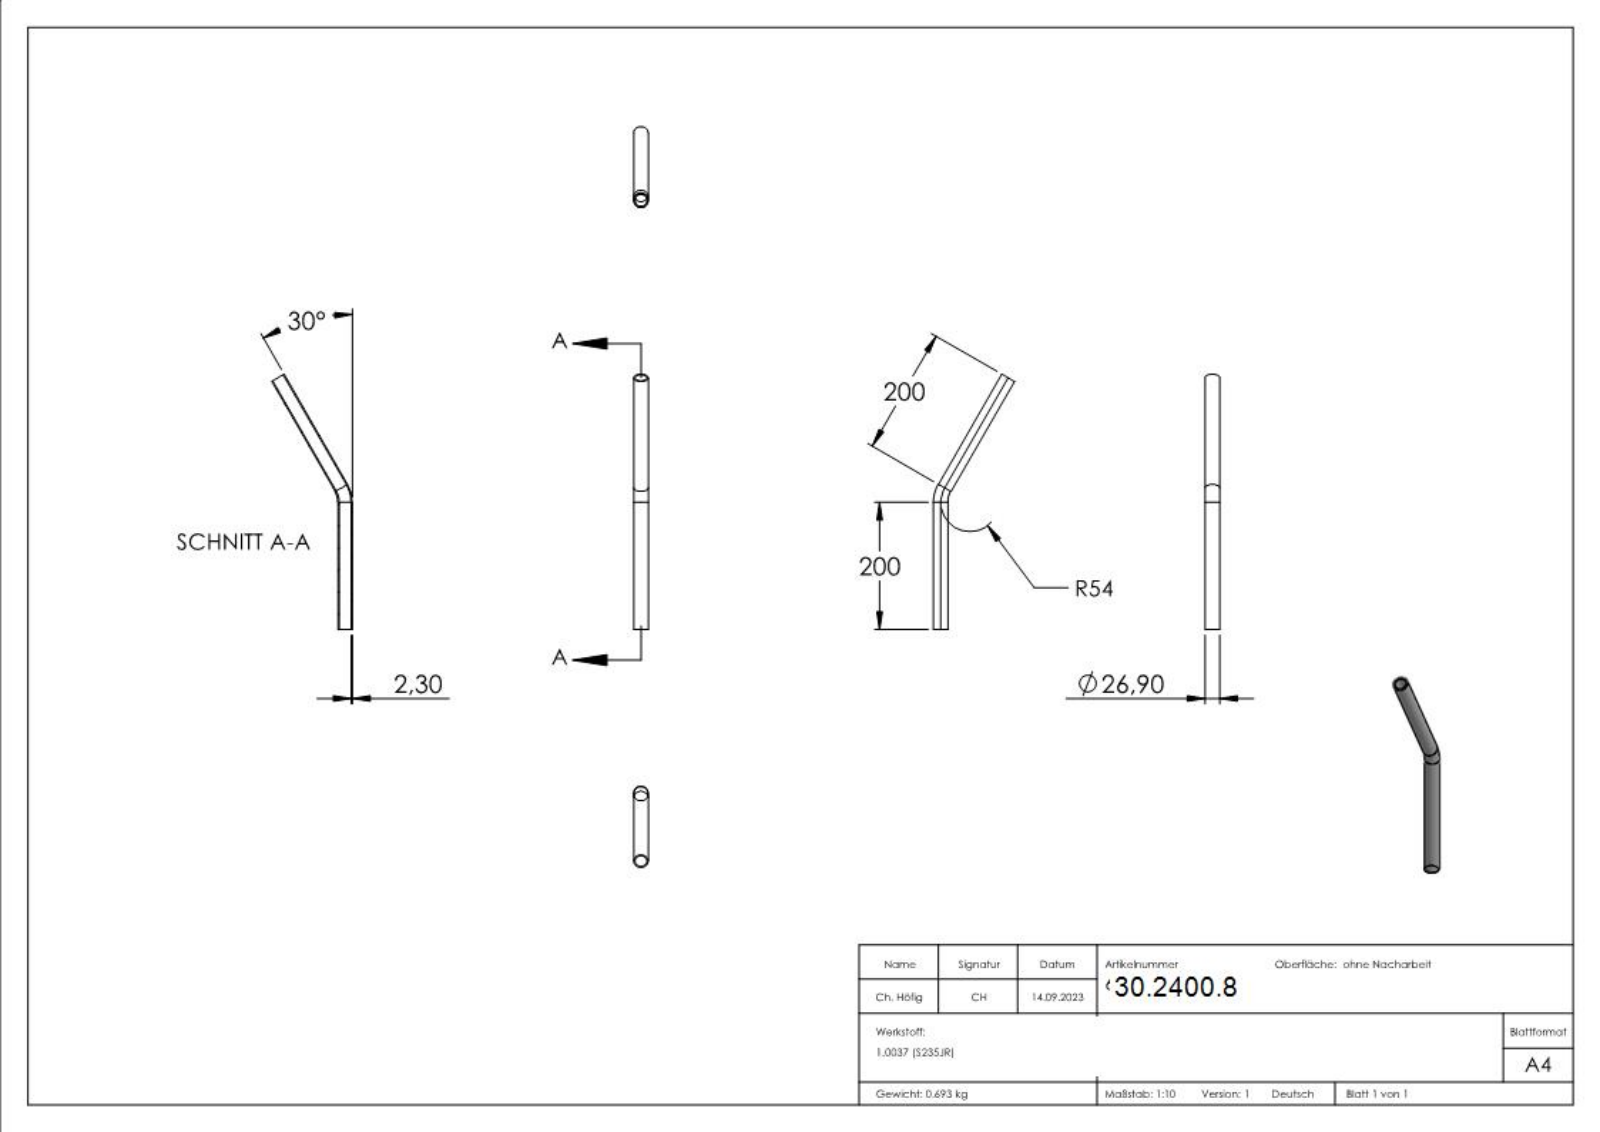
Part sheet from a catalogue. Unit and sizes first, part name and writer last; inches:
Units: inches
Overall size (bounding box): 18.656 × 5.916 × 1.059
Round holes (diameter × count): ⌀0.878 ×2
Round bosses / shafts (diameter × count): ⌀1.059 ×2
Main face-to-face distances: 0.021, 0.023, 0.013, 0.015, 0.013, 0.019, 0.012, 0.014, 0.016, 0.021
Volume: 5.424 in³ · Surface area: 120.3 in²
Bodies: 1 solid, 223 faces (102 planar, 4 cylindrical, 117 other)
Part name (STEP PRODUCT): 6965-030
STEP written by: SolidWorks 2018 (CONFIG_CONTROL_DESIGN)
